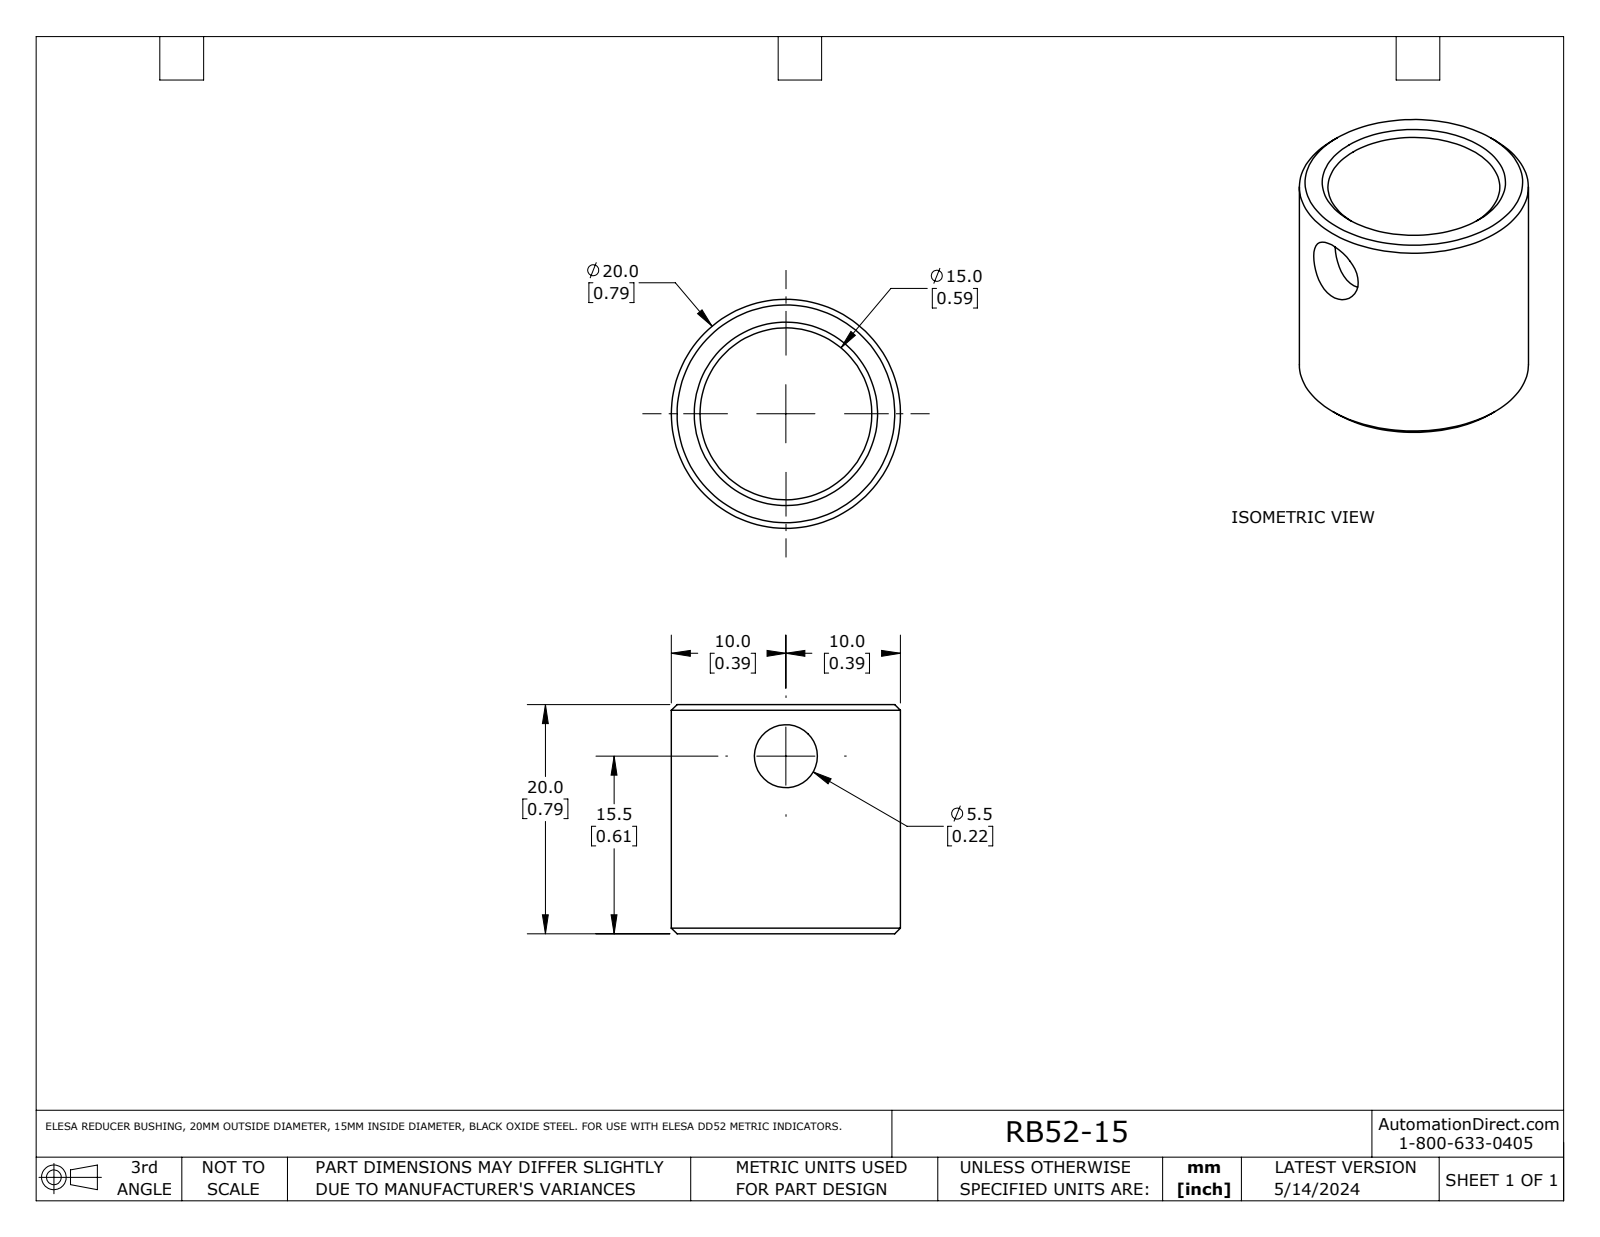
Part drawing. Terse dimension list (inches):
name: RB52-15
written by: SolidWorks 2023 (AUTOMOTIVE_DESIGN)
unit: in
bodies: 1 solid, 9 faces (2 planar, 3 cylindrical, 4 other)
size: 0.787 × 0.787 × 0.787
volume: 0.162 in³; area: 3.729 in²
holes: 1× ⌀0.217, 1× ⌀0.591
bosses: 1× ⌀0.787
face distances: 0.787
